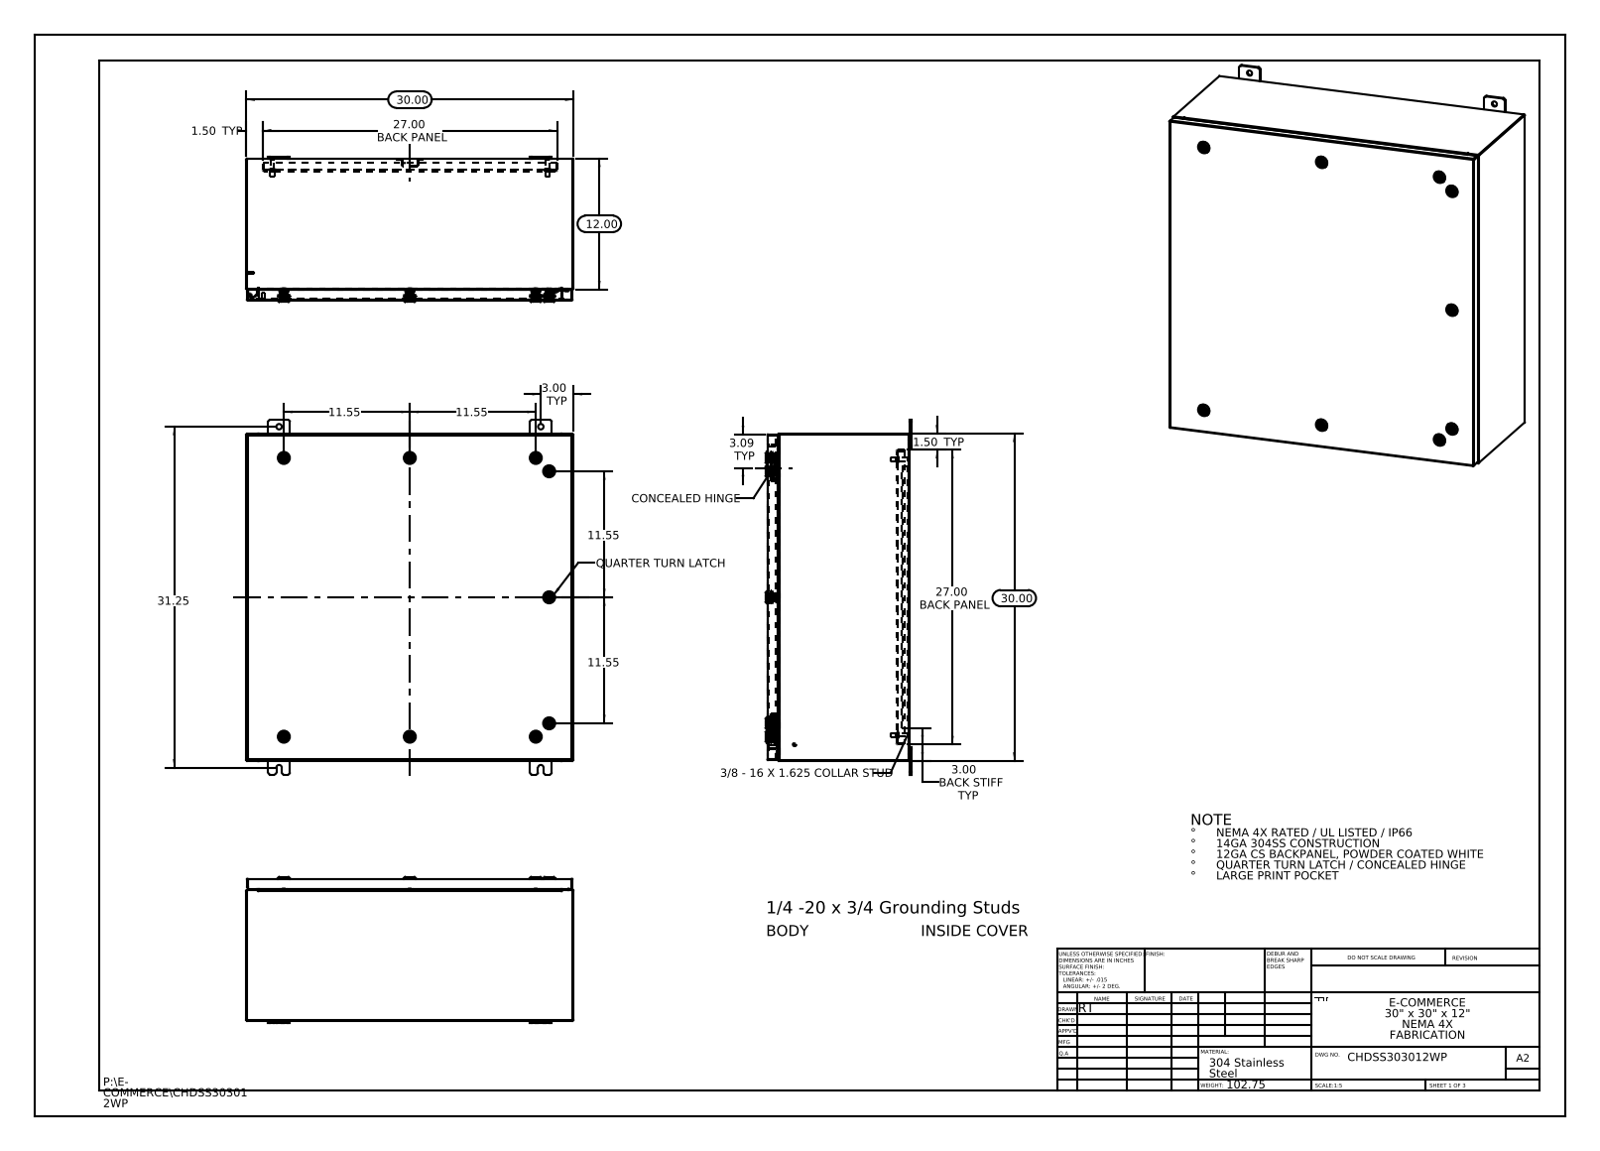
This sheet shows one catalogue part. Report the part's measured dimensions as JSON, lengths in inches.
{"part_name": "CHDSS303012WP Body; CHDSS303012WP Mounting Feet; Housing-211301-IB-Industrilas_Housing-211301-IB-Industrilas; CHDSS303012WP Enclosure Stiffener (+8 more)", "step_written_by": "SolidWorks 2013 (CONFIG_CONTROL_DESIGN)", "units": "inches", "bodies": {"solids": 74, "faces": 7916, "planar": 2280, "cylindrical": 2462, "other": 3174}, "overall_size": [32.5, 30, 13.356], "volume_in3": 364.7, "surface_area_in2": 9110, "round_holes": [[0.197, 9], [0.394, 9], [0.4, 9], [0.63, 9], [0.787, 9], [0.5, 8], [0.136, 4], [0.211, 1]], "round_bosses_or_shafts": [[0.236, 11], [1.102, 9], [0.78, 9], [0.626, 9], [0.61, 9], [0.531, 9], [0.392, 9], [0.114, 9]], "partial_cylinders_radius": [[0.006, 297], [0.118, 297], [0.028, 108], [0.02, 36], [0.197, 36], [0.013, 26], [0.19, 24], [0.088, 22]], "face_to_face_distances": [0.075, 29.925, 0.074, 13.01, 12.935, 12.936, 12.861, 0.104, 1, 1.075], "hole_center_spacings": [11.55, 28.039, 12.834, 23.1, 24.356, 25.55, 0.688, 1.858]}
